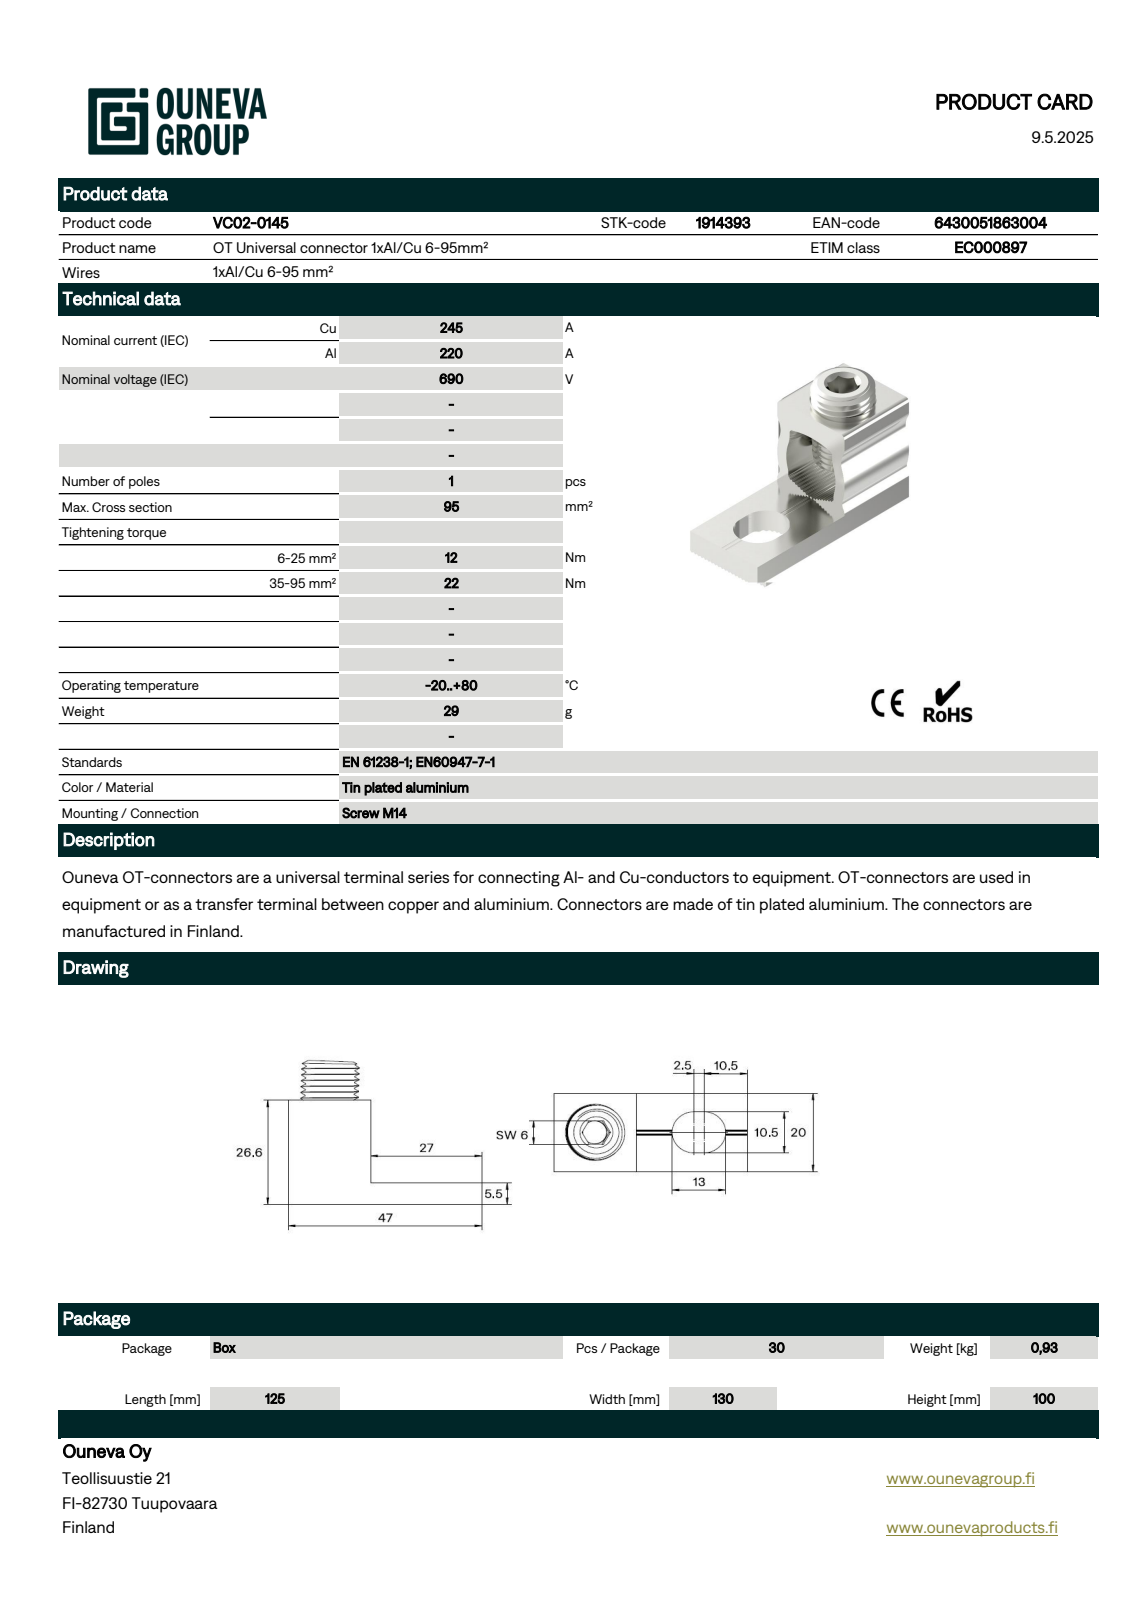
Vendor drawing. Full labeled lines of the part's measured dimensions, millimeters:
Part name (STEP PRODUCT): Liitinrunko_OT_1x95
STEP written by: Creo Elements/Direct Modeling 20.6A 14-Oct-2023 (C) Parametric Technology GmbH (AUTOMOTIVE_DESIGN)
Units: millimetres
Bodies: 1 solid, 225 faces (86 planar, 133 cylindrical, 6 other)
Overall size (bounding box): 47 × 33.32 × 20
Volume: 10 679 mm³ · Surface area: 5 742 mm²
Round bosses / shafts (diameter × count): ⌀14 ×1
Partial cylindrical surfaces — rounded edges, fillets, slot ends (radius × count): R0.25 ×68, R0.15 ×8, R1 ×4, R2 ×4, R0.25 ×2, R0.5 ×2, R2.5 ×2, R5.2 ×2
Main face-to-face distances: 20, 21.1, 1.45, 3.62, 2.17, 0.72, 5.07, 7.24, 2.9, 5.79
